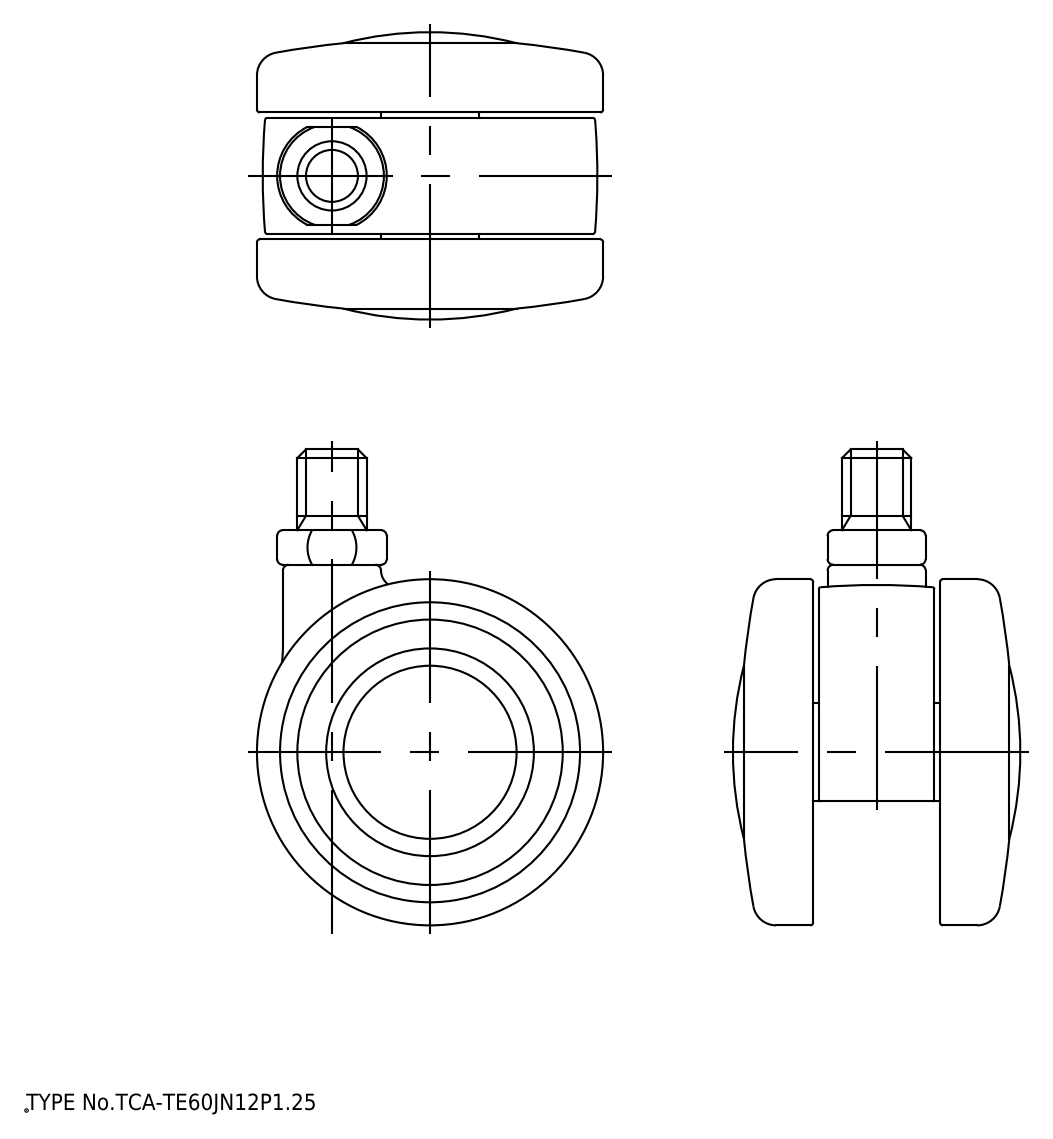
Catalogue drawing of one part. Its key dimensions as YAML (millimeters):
part_name: "TCA-TE60J_Body; TCA-TE60J_Wheel; TCA-TE60JN12_Shaft"
step_written_by: "spGate 18.9.1 (****-****-****-****) (AUTOMOTIVE_DESIGN)"
units: millimeters
bodies: {solids: 4, faces: 189, planar: 46, cylindrical: 75, other: 68}
overall_size: [82.5, 60, 49.14]
volume: 86388
surface_area: 31861
round_holes:
  - {diameter: 8, count: 1}
  - {diameter: 9.3, count: 1}
  - {diameter: 10.7, count: 1}
  - {diameter: 20, count: 1}
  - {diameter: 30.2, count: 1}
  - {diameter: 45, count: 1}
round_bosses_or_shafts:
  - {diameter: 60, count: 1}
  - {diameter: 36, count: 1}
  - {diameter: 29.9, count: 1}
  - {diameter: 18, count: 1}
  - {diameter: 17, count: 1}
  - {diameter: 12, count: 1}
  - {diameter: 10.5, count: 1}
  - {diameter: 6.5, count: 1}
partial_cylinders:
  - {radius: 0.3, count: 5}
  - {radius: 1, count: 3}
  - {radius: 2, count: 3}
  - {radius: 10, count: 1}
  - {radius: 10.5, count: 1}
  - {radius: 26.5, count: 1}
  - {radius: 29, count: 1}
face_to_face_distances: [2, 19, 7, 5, 24, 26, 11, 30.5, 28.5, 0.5]
